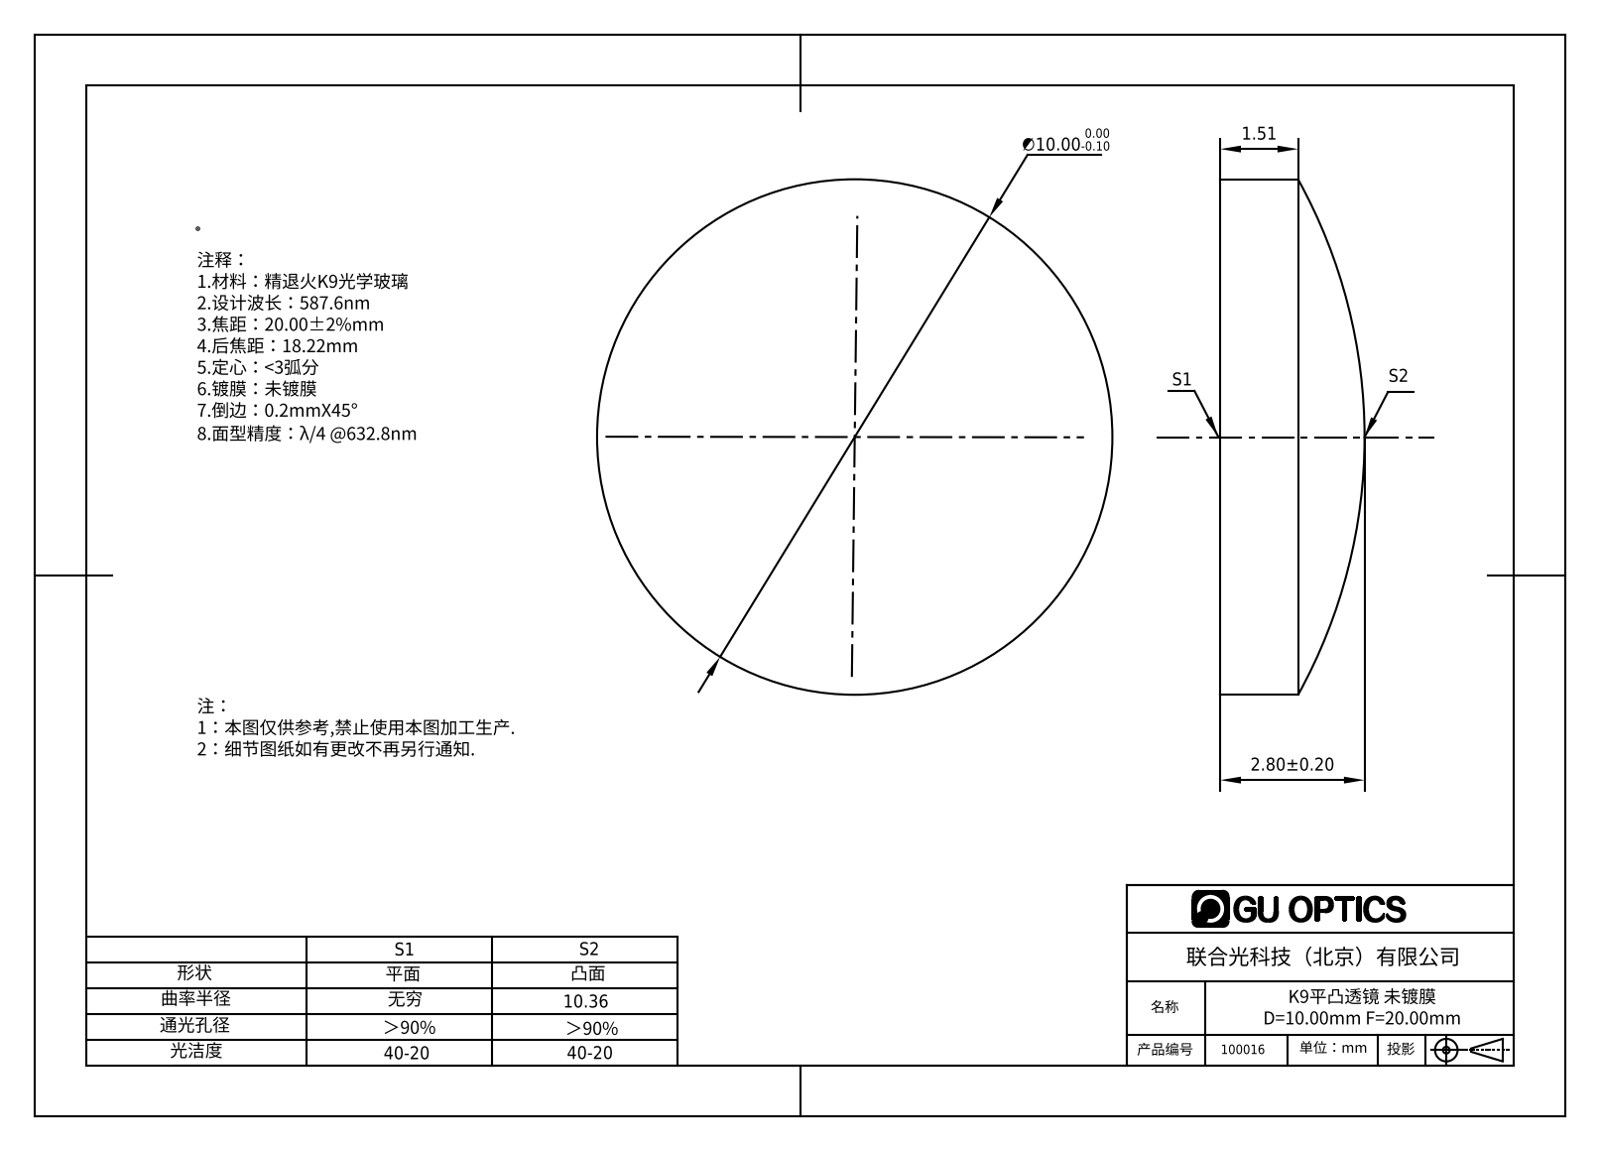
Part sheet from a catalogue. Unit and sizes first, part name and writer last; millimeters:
Units: millimetres
Overall size (bounding box): 10 × 10 × 2.8
Round bosses / shafts (diameter × count): ⌀10 ×1
Volume: 170 mm³ · Surface area: 210 mm²
Bodies: 1 solid, 5 faces (1 planar, 2 cylindrical, 2 other)
Part name (STEP PRODUCT): 100016
STEP written by: SolidWorks 2016 (AUTOMOTIVE_DESIGN)
